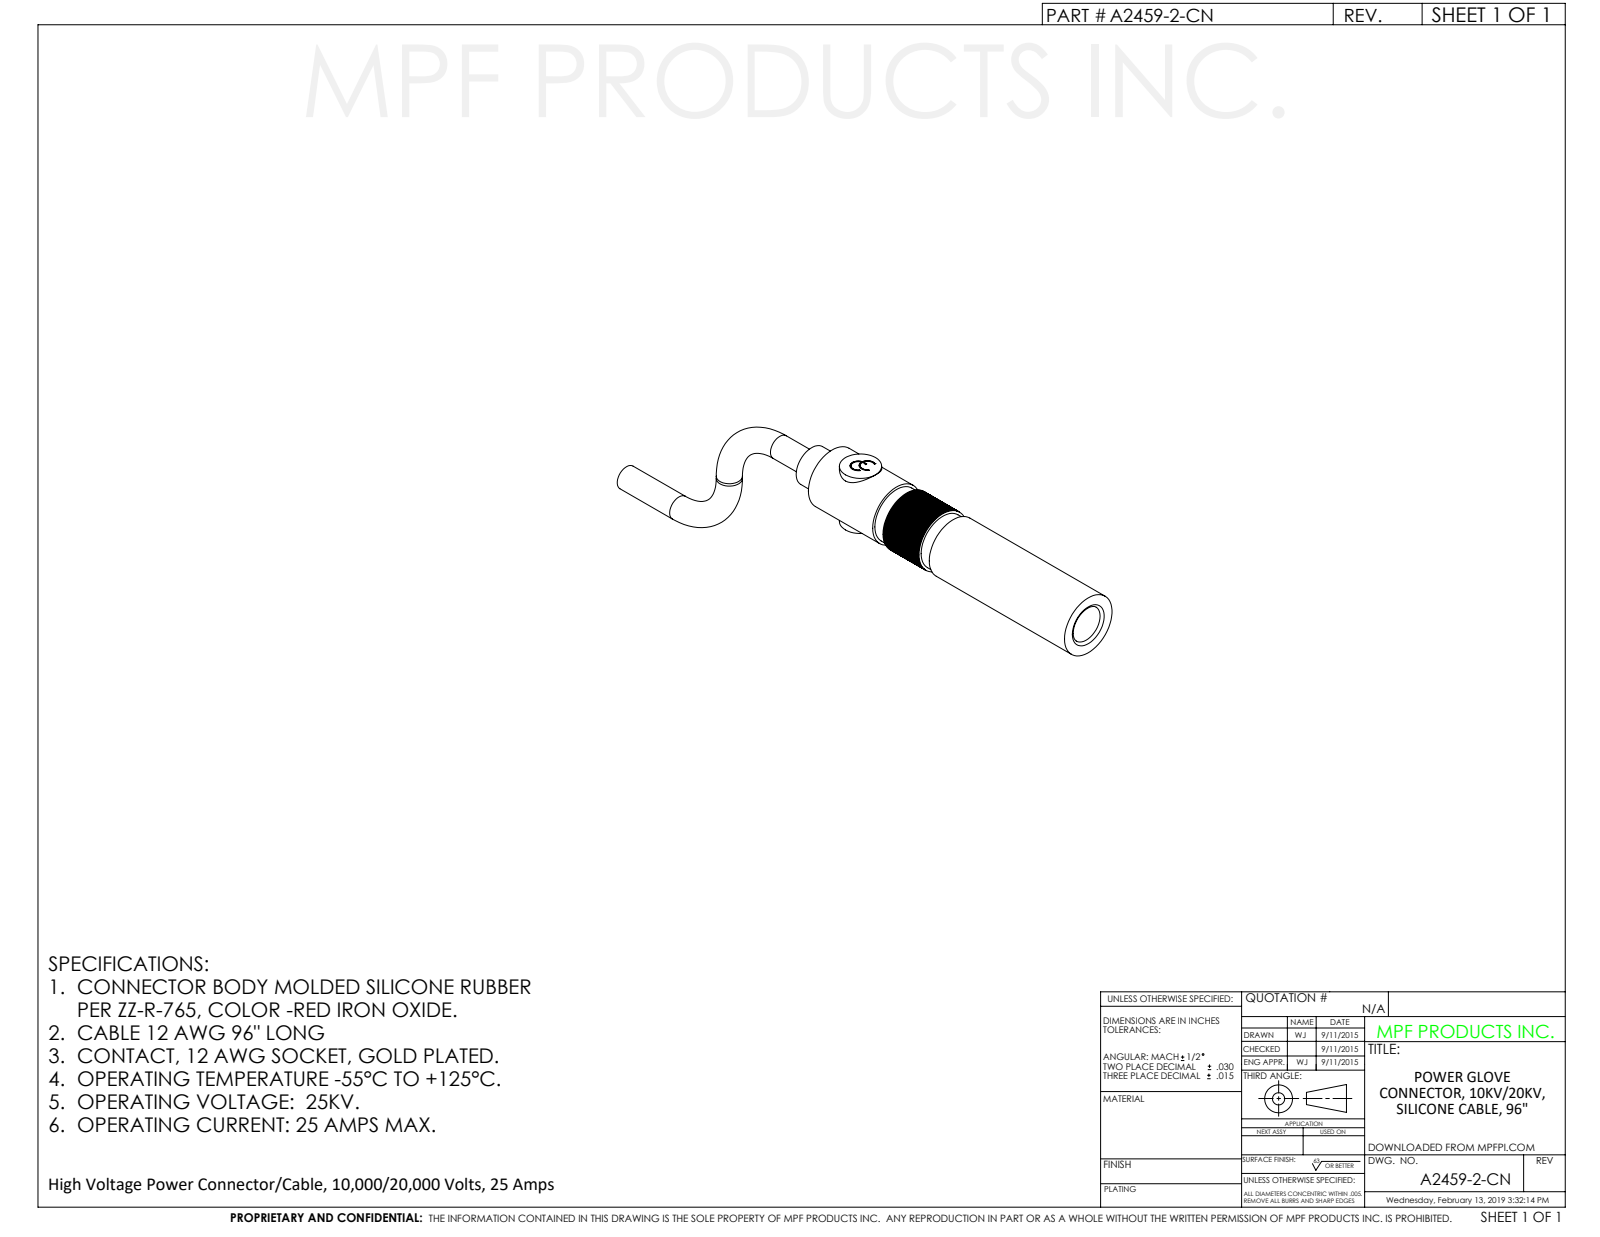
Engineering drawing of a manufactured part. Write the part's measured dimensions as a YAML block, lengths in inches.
part_name: "A2459-2"
step_written_by: "SolidWorks 2012 (CONFIG_CONTROL_DESIGN)"
units: inches
bodies: {solids: 1, faces: 519, planar: 15, cylindrical: 18, other: 486}
overall_size: [3.079, 0.694, 0.455]
volume: 0.347
surface_area: 5.395
round_holes:
  - {diameter: 0.28, count: 1}
  - {diameter: 0.287, count: 1}
  - {diameter: 0.313, count: 1}
round_bosses_or_shafts:
  - {diameter: 0.445, count: 1}
  - {diameter: 0.427, count: 1}
  - {diameter: 0.282, count: 1}
  - {diameter: 0.219, count: 1}
face_to_face_distances: [2.474, 1.43, 1.044, 0.481, 0.193, 1.623, 2.667, 1.893, 1.7, 0.27]
